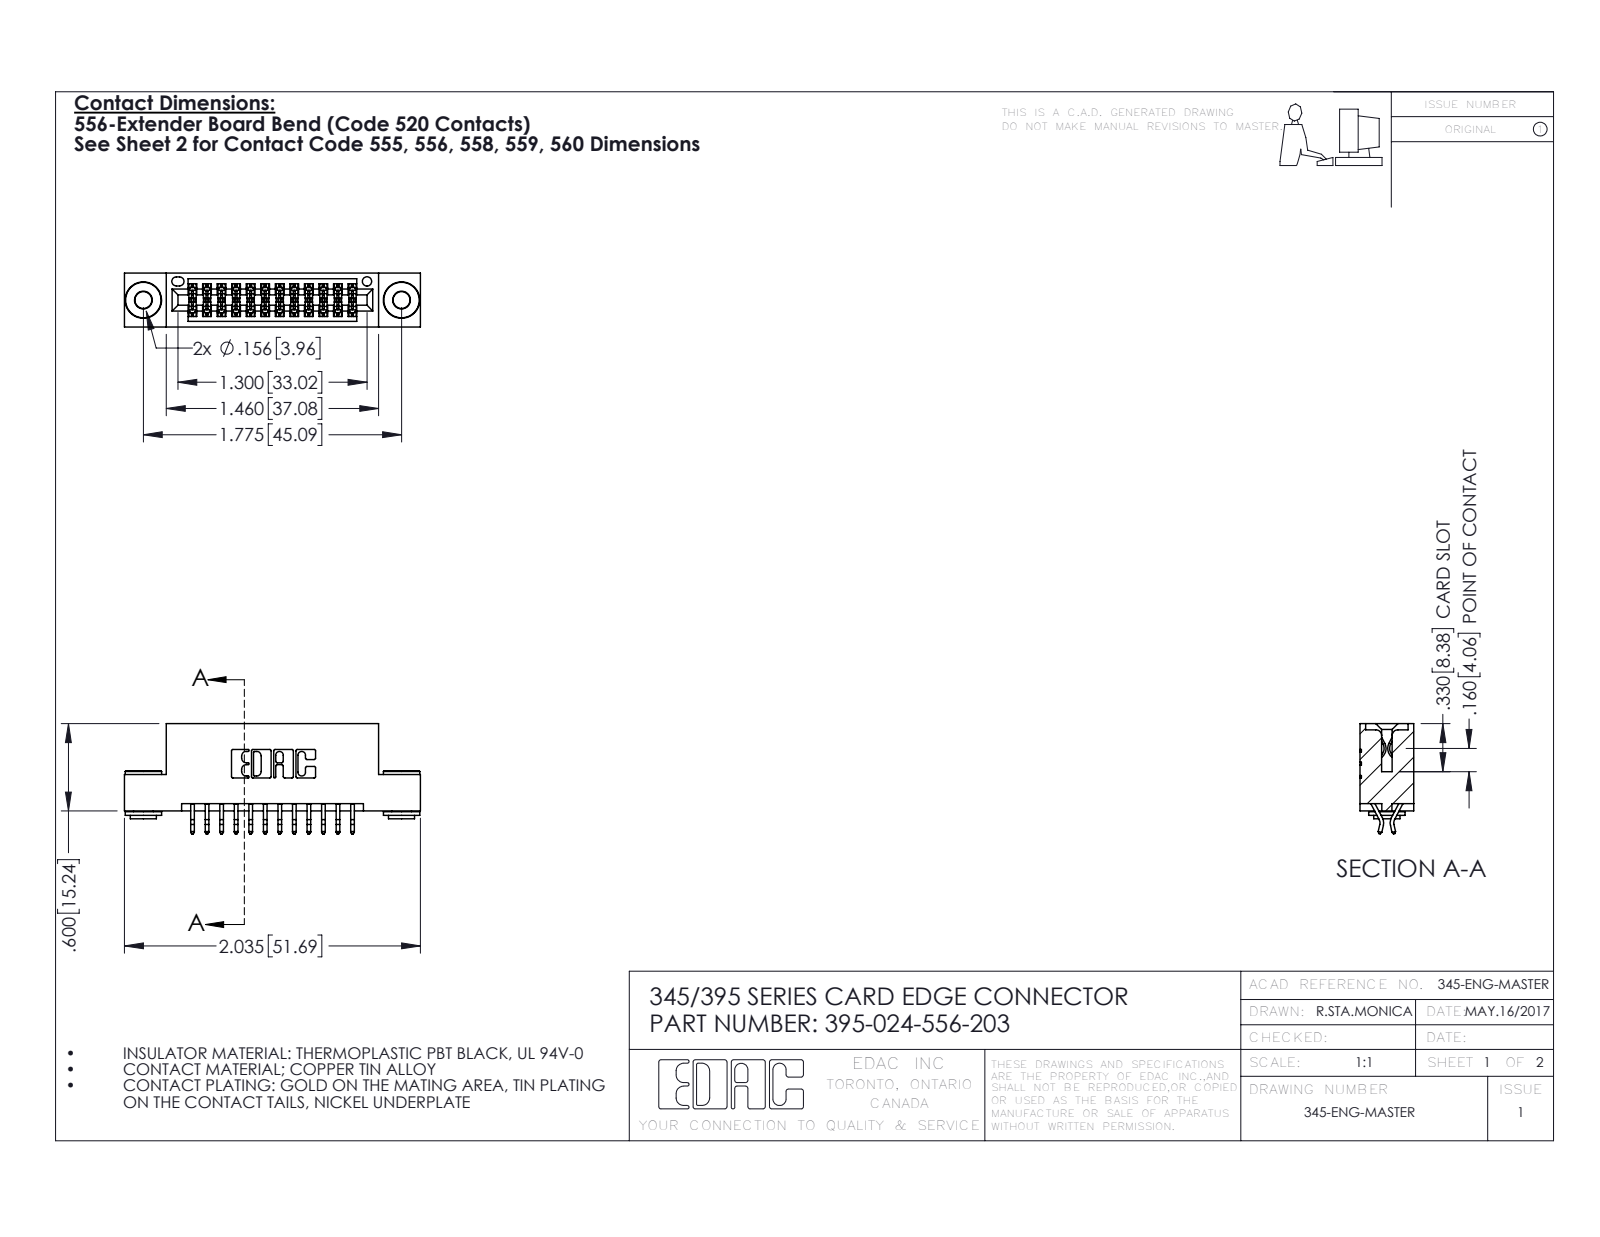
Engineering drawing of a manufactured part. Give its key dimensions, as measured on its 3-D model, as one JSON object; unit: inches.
{"part_name": "345 Part_Flush Mounting Lugs - 0.156 Dia-TH; 345-250-002_345-250-002-102; 395-024-556-203; 345-292-001_556 Tail", "step_written_by": "SolidWorks 2016 (CONFIG_CONTROL_DESIGN)", "units": "inches", "bodies": {"solids": 27, "faces": 1508, "planar": 978, "cylindrical": 522, "other": 8}, "overall_size": [2.035, 0.757, 0.37], "volume_in3": 0.291, "surface_area_in2": 10.29, "round_holes": [[0.116, 2], [0.156, 2], [0.064, 1]], "round_bosses_or_shafts": [[0.25, 2], [0.18, 2], [0.136, 2]], "partial_cylinders_radius": [[0.006, 36], [0.01, 22], [0.007, 6], [0.031, 6], [0.026, 3], [0.01, 2], [0.014, 2], [0.019, 2]], "face_to_face_distances": [0.2, 0.072, 0.298, 0.37, 0.025, 0.098, 0.272, 0.225, 0.1, 0.3], "hole_center_spacings": [0.27, 1.543, 1.775]}
